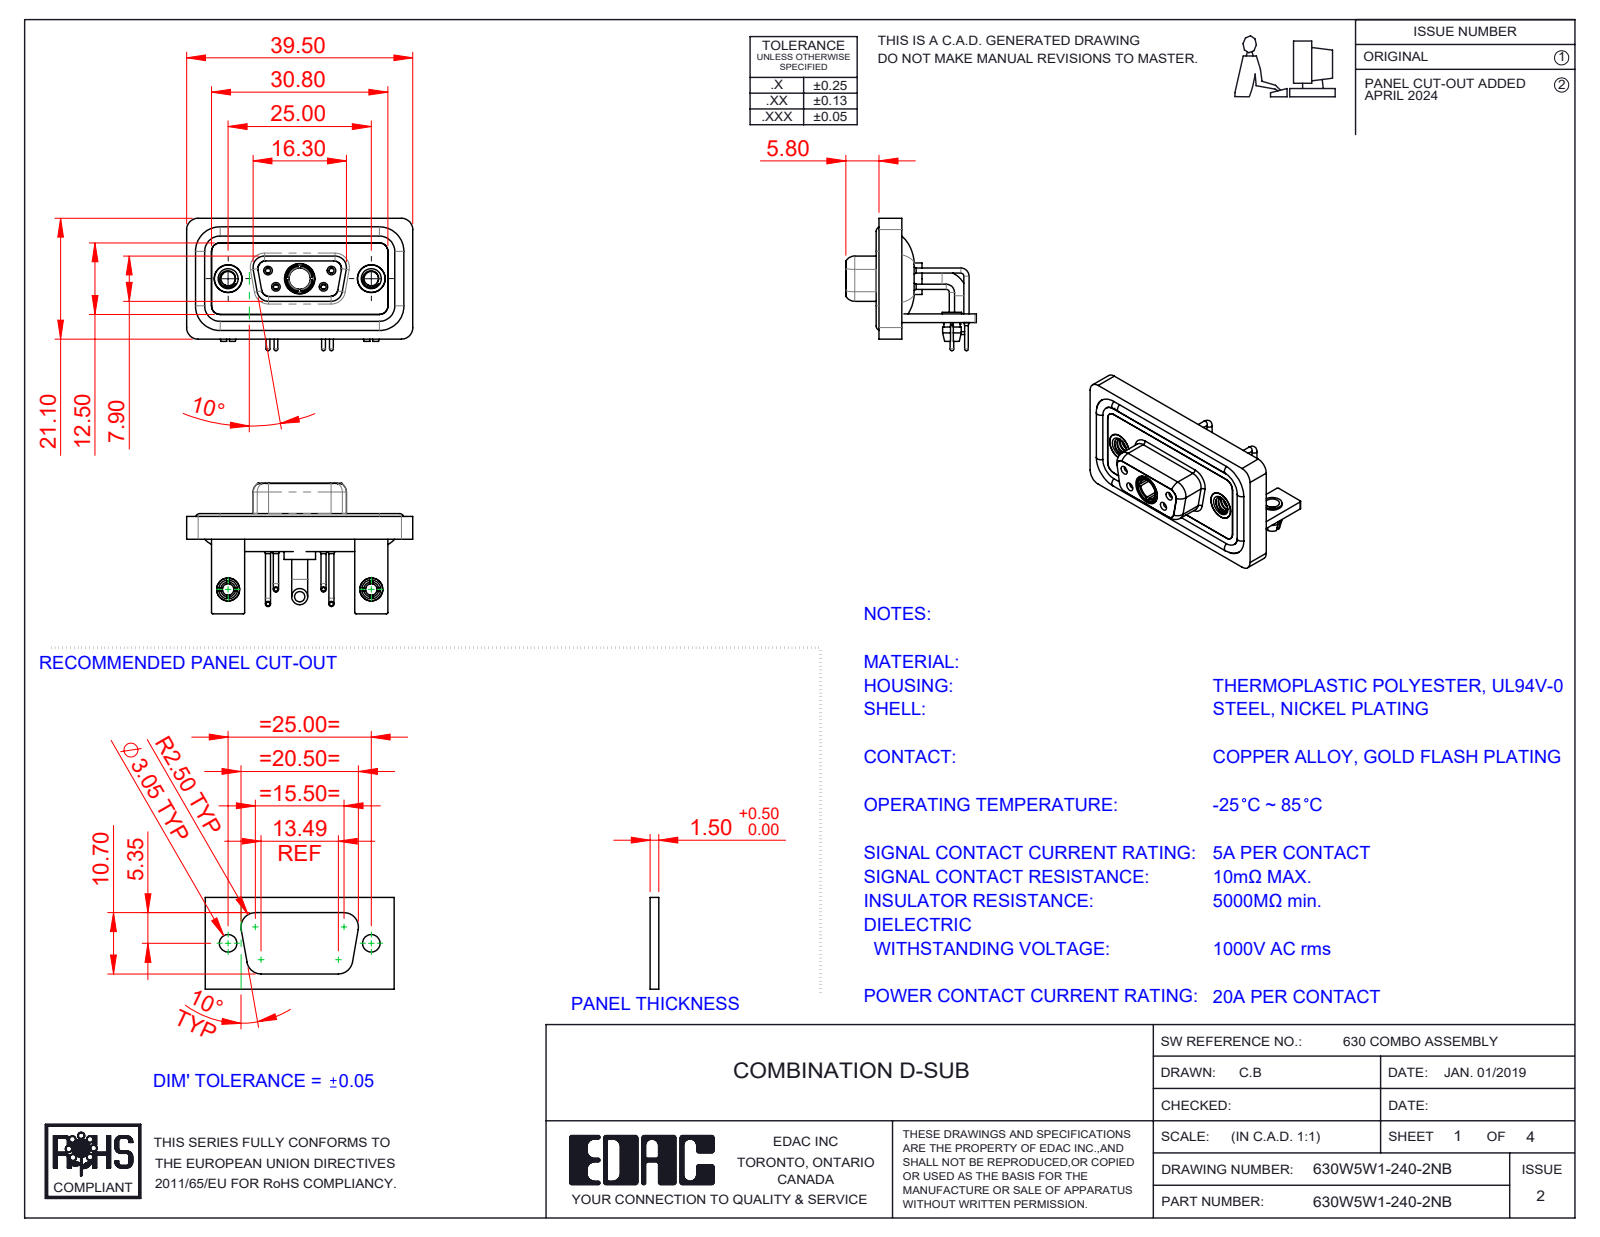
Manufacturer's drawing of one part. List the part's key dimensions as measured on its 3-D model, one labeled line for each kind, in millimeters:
Part name (STEP PRODUCT): 630Combo Board Lock_50 Contacts; 630W5W1-140-2NB; Power Socket_20A RA; 630Combo Shell Rear_09 Contacts (+7 more)
STEP written by: SolidWorks 2023 (CONFIG_CONTROL_DESIGN)
Units: millimetres
Bodies: 17 solids, 810 faces (262 planar, 359 cylindrical, 189 other)
Overall size (bounding box): 39.5 × 23.12 × 22.8
Volume: 5 224 mm³ · Surface area: 8 792 mm²
Round holes (diameter × count): ⌀2 ×6, ⌀0.9 ×4, ⌀1.1 ×4, ⌀1.5 ×4, ⌀2.5 ×4, ⌀4.85 ×3, ⌀1.6 ×2, ⌀1.7 ×2, ⌀3.2 ×2, ⌀4 ×2, ⌀4.05 ×2, ⌀5 ×2
Round bosses / shafts (diameter × count): ⌀1.6 ×6, ⌀0.9 ×4, ⌀0.65 ×4, ⌀4.95 ×2, ⌀4.8 ×2, ⌀4 ×2, ⌀3.4 ×2, ⌀3.3 ×2
Partial cylindrical surfaces — rounded edges, fillets, slot ends (radius × count): R2 ×19, R1.5 ×18, R0.25 ×16, R1.35 ×8, R1.6 ×8, R0.5 ×5, R0.6 ×4, R0.65 ×4
Main face-to-face distances: 0.4, 2.9, 1.5, 1.8, 1.1, 3.7, 1.6, 0.8, 2.5, 3.1
Hole centre spacings: 3.16, 5.72, 7.1, 12.5, 18.1, 25, 4.39, 4.4
